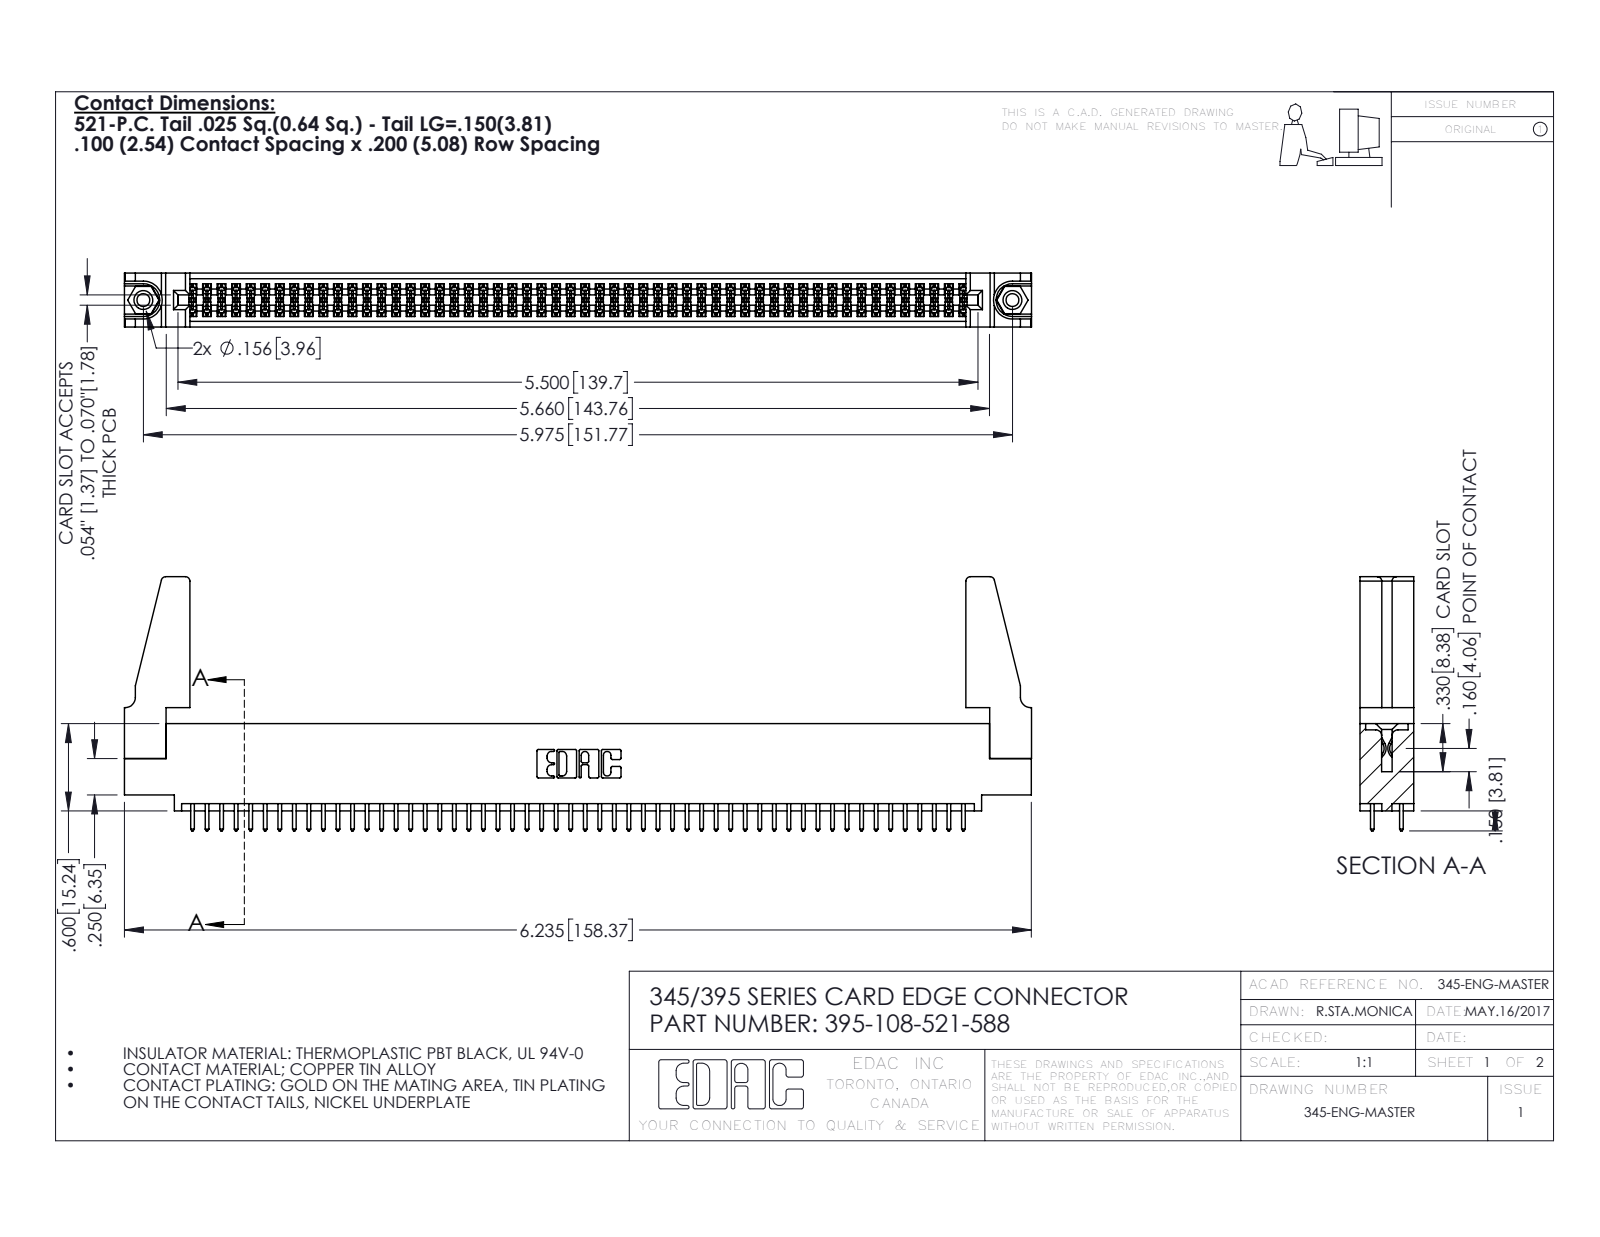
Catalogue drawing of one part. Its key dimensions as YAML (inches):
part_name: "345-250-001_345-250-001-102; 345-220-078_345-220-088; 395-108-521-588; 345-292-001_345-293-121 (+1 more)"
step_written_by: "SolidWorks 2016 (CONFIG_CONTROL_DESIGN)"
units: inches
bodies: {solids: 113, faces: 5654, planar: 3720, cylindrical: 1918, other: 16}
overall_size: [6.236, 1.747, 0.37]
volume: 1.137
surface_area: 40.14
round_holes:
  - {diameter: 0.089, count: 2}
  - {diameter: 0.125, count: 2}
  - {diameter: 0.156, count: 2}
  - {diameter: 0.064, count: 1}
round_bosses_or_shafts:
  - {diameter: 0.155, count: 2}
partial_cylinders:
  - {radius: 0.006, count: 162}
  - {radius: 0.01, count: 108}
  - {radius: 0.01, count: 22}
  - {radius: 0.03, count: 8}
  - {radius: 0.007, count: 6}
  - {radius: 0.031, count: 6}
  - {radius: 0.026, count: 3}
  - {radius: 0.014, count: 2}
face_to_face_distances: [0.072, 0.298, 0.37, 0.2, 0.098, 0.272, 0.025, 0.225, 0.175, 0.149]
hole_center_spacings: [0.27, 5.739, 5.975]
